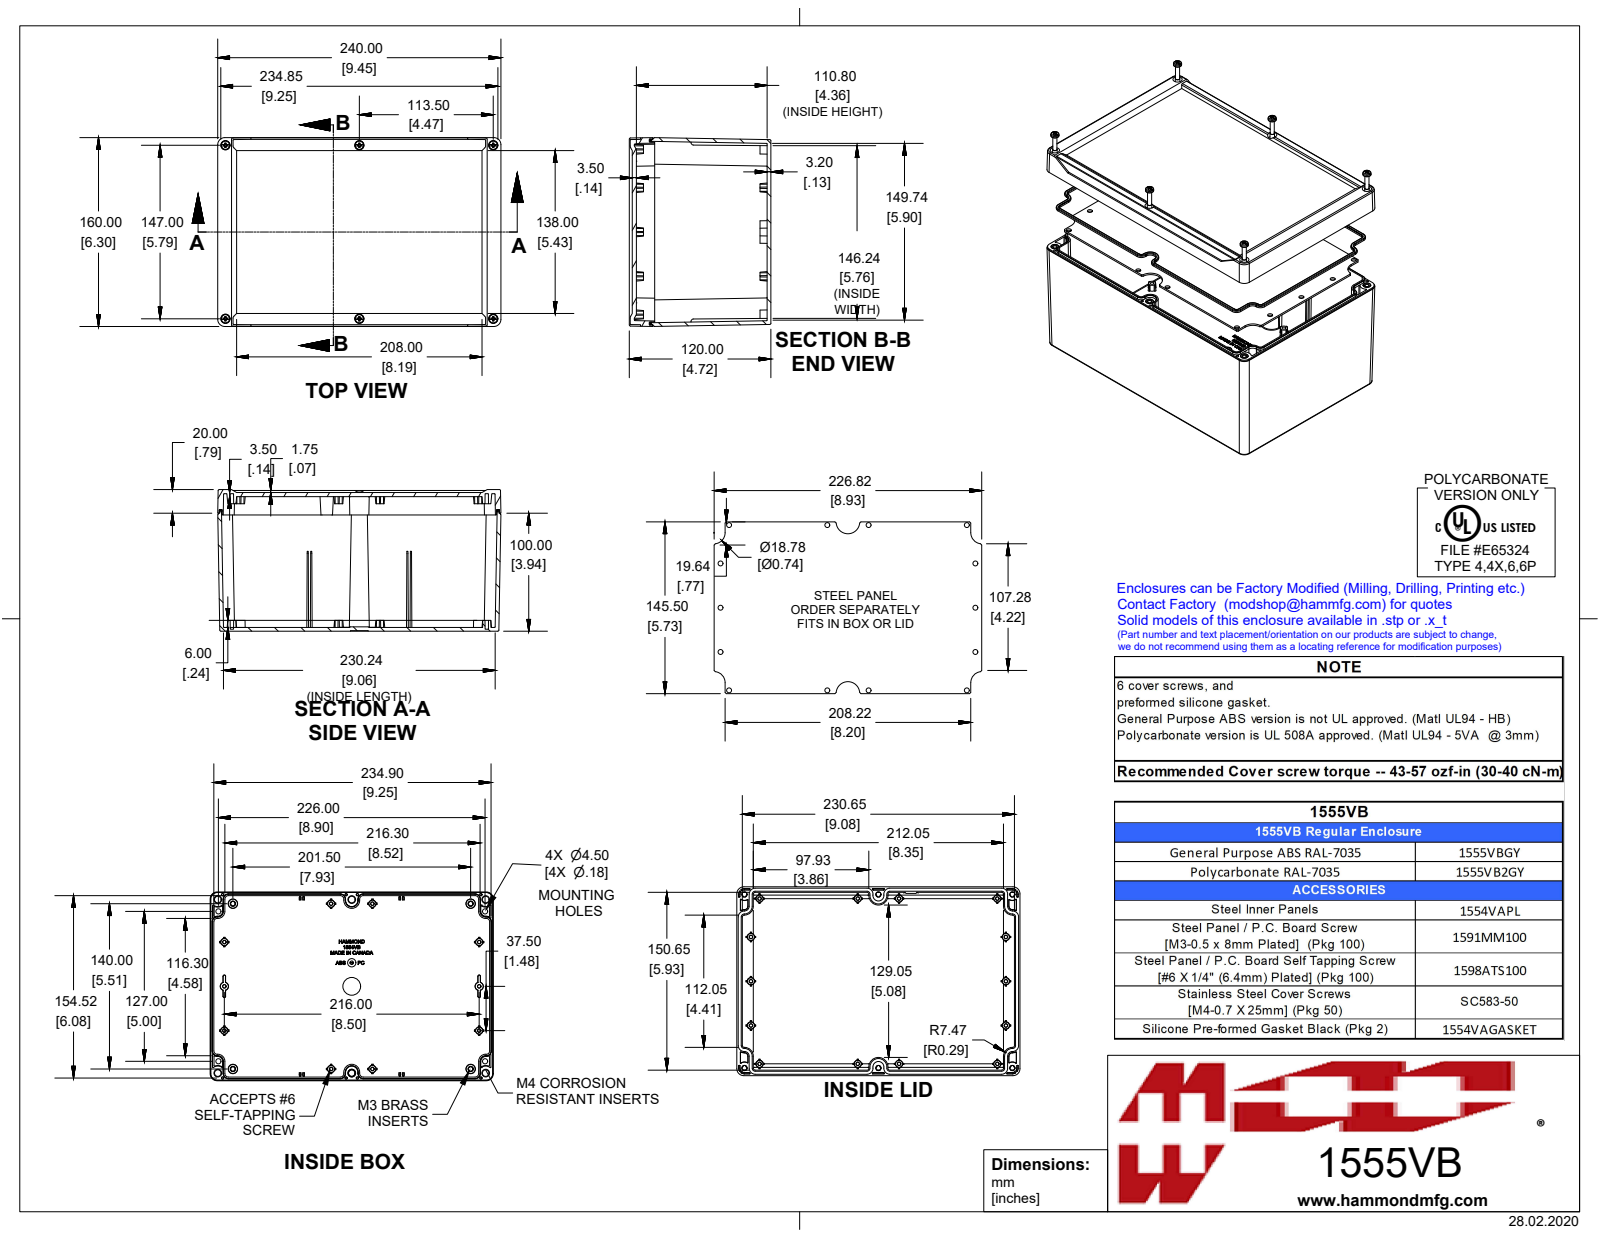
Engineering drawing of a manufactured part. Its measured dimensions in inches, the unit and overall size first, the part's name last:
Units: inches
Overall size (bounding box): 9.449 × 6.299 × 4.724
Round holes (diameter × count): ⌀0.128 ×6, ⌀0.221 ×5, ⌀0.256 ×5, ⌀0.097 ×4, ⌀0.276 ×1, ⌀0.591 ×1
Round bosses / shafts (diameter × count): ⌀0.272 ×6, ⌀0.25 ×6, ⌀0.218 ×6, ⌀0.21 ×6, ⌀0.152 ×6, ⌀0.137 ×6, ⌀0.19 ×4, ⌀0.154 ×4
Partial cylindrical surfaces — rounded edges, fillets, slot ends (radius × count): R0.02 ×55, R0.012 ×28, R0.1 ×12, R0.195 ×12, R0.059 ×8, R0.168 ×8, R0.236 ×8, R0.039 ×6
Main face-to-face distances: 0.126, 0.138, 4.362, 4.488, 4.626, 4.5, 0.185, 6.114, 5.988, 9.323
Hole centre spacings: 0.52, 3.969, 4.469, 4.83, 5.324, 5.672, 6.903, 7.312
Volume: 36.04 in³ · Surface area: 617.8 in²
Bodies: 19 solids, 2827 faces (1281 planar, 493 cylindrical, 1053 other)
Part name (STEP PRODUCT): 1555VB2GY
STEP written by: SolidWorks 2019 (AUTOMOTIVE_DESIGN)
